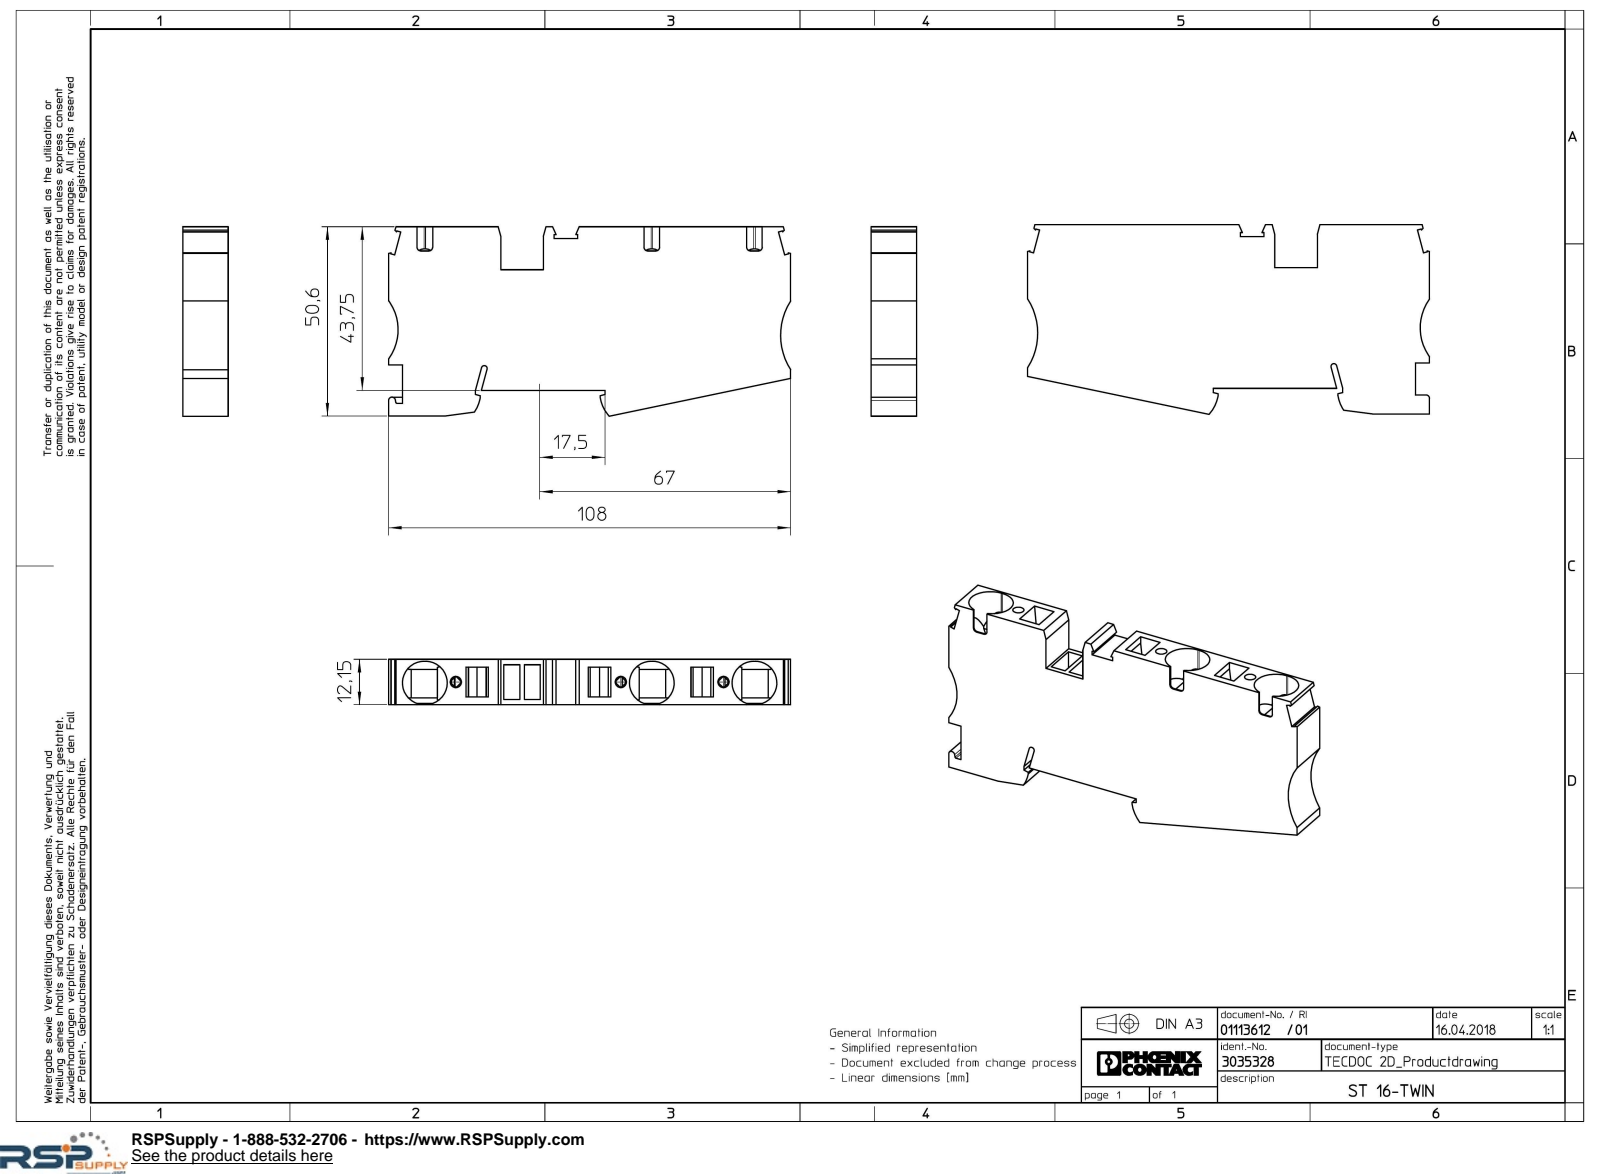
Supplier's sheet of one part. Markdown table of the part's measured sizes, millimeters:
| quantity | value |
| --- | --- |
| part name | ST_16_TWIN_BU-select |
| STEP written by | Creo Elements/Direct Modeling 20.1A 29-Sep-2018 (C) Parametric Technology GmbH (AUTOMOTIVE_DESIGN) |
| units | millimeters |
| bodies | 1 solid, 206 faces (159 planar, 41 cylindrical, 6 other) |
| overall size | 107.7 × 50.69 × 12.15 |
| volume | 48 135 mm³ |
| surface area | 18 346 mm² |
| round holes (diameter × count) | 3 × 3 |
| partial cylindrical surfaces (radius × count) | 0.5 × 12, 1 × 6, 5.8 × 6, 9.5 × 2, 0.3 × 1, 0.7 × 1, 0.8 × 1, 0.9 × 1 |
| main face-to-face distances | 12.15, 43.75, 0.6, 2.67, 9.48, 10.27, 7.6, 1.88, 7.05, 6.85 |
| hole center spacings | 27.5, 44.2, 71.7 |
